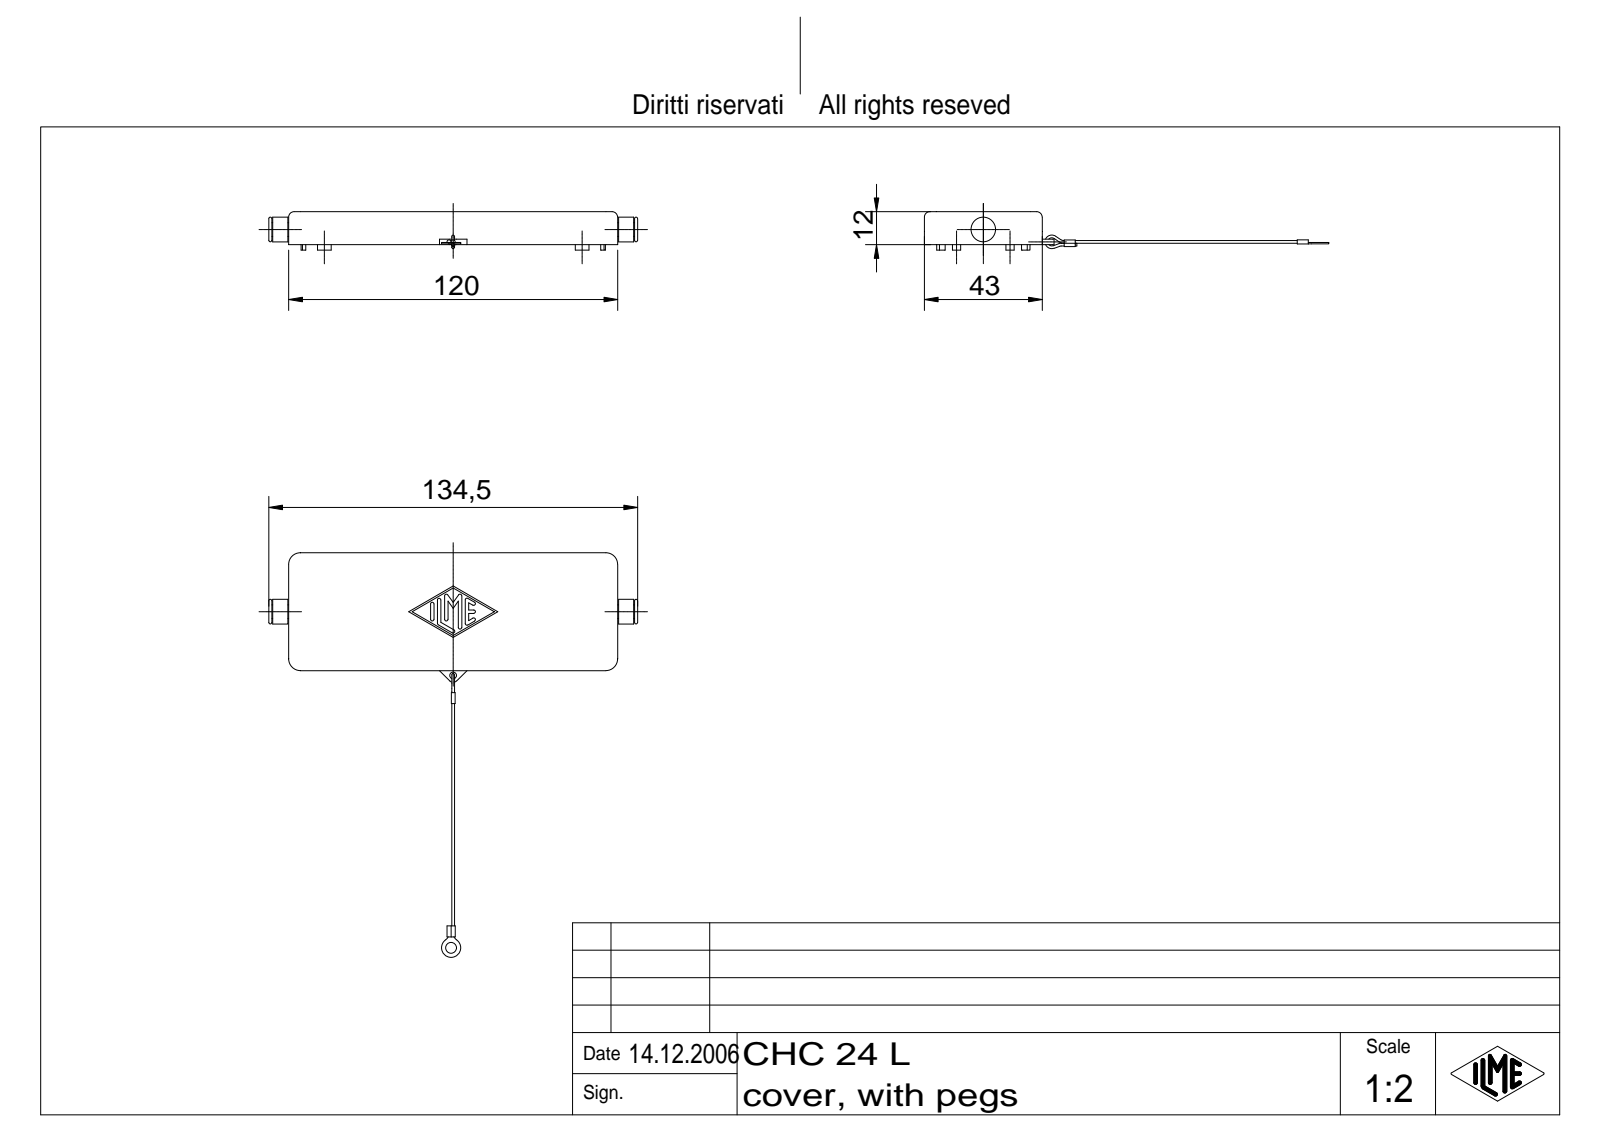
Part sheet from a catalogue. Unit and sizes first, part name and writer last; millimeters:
Units: millimetres
Overall size (bounding box): 147.5 × 134.5 × 14
Round holes (diameter × count): ⌀2.5 ×1, ⌀4 ×1
Round bosses / shafts (diameter × count): ⌀1 ×4, ⌀9 ×1, ⌀7 ×1, ⌀5 ×1
Partial cylindrical surfaces — rounded edges, fillets, slot ends (radius × count): R0.62 ×14, R2 ×8, R0.7 ×4, R4.3 ×4, R0.75 ×2, R1 ×2, R3 ×2, R1.75 ×1
Main face-to-face distances: 3, 4.5, 38.5, 12, 9, 43, 34, 115.5, 120, 111
Hole centre spacings: 99.25
Volume: 29 150 mm³ · Surface area: 18 088 mm²
Bodies: 2 solids, 230 faces (95 planar, 75 cylindrical, 60 other)
Part name (STEP PRODUCT): CHC 24 L
STEP written by: Autodesk Inventor 7 (AUTOMOTIVE_DESIGN)
